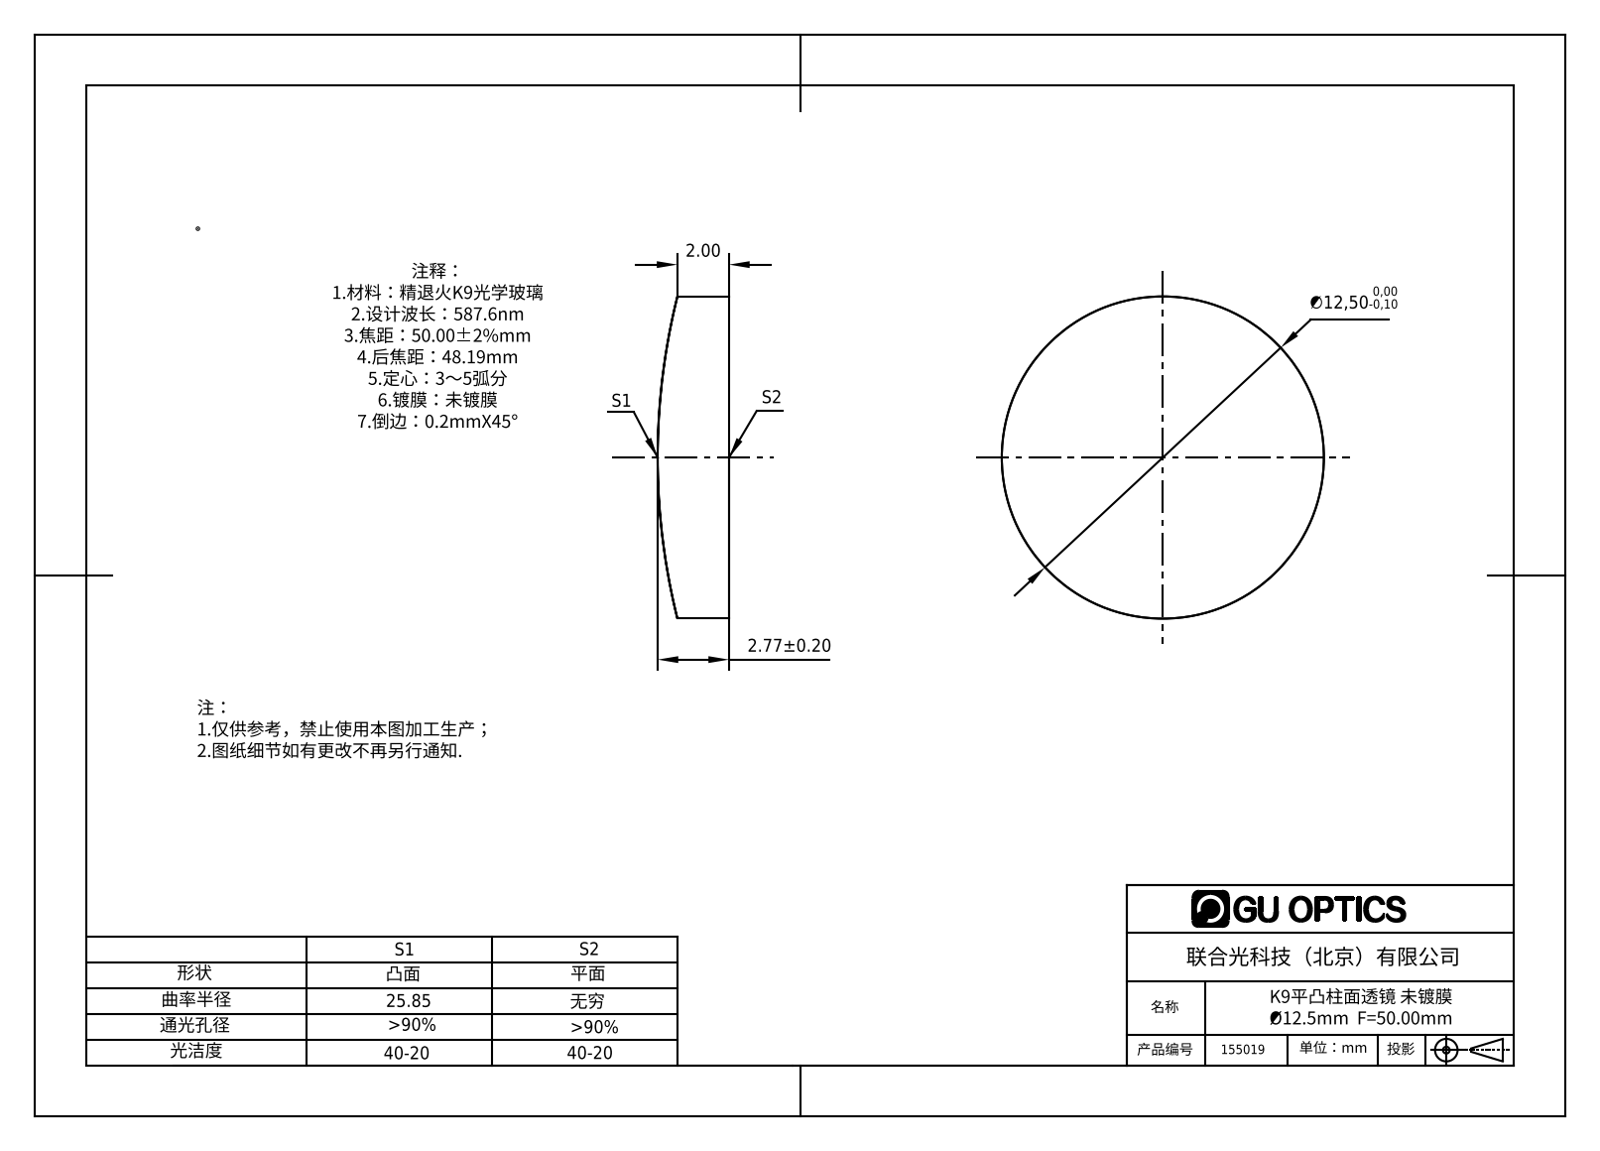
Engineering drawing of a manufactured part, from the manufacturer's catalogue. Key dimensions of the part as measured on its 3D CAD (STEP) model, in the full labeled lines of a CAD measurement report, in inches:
Part name (STEP PRODUCT): 155019
STEP written by: SolidWorks 2016 (AUTOMOTIVE_DESIGN)
Units: inches
Bodies: 1 solid, 4 faces (1 planar, 3 cylindrical, 0 other)
Overall size (bounding box): 0.492 × 0.492 × 0.109
Volume: 0.019 in³ · Surface area: 0.527 in²
Round bosses / shafts (diameter × count): ⌀0.492 ×1
Partial cylindrical surfaces — rounded edges, fillets, slot ends (radius × count): R1.018 ×1
